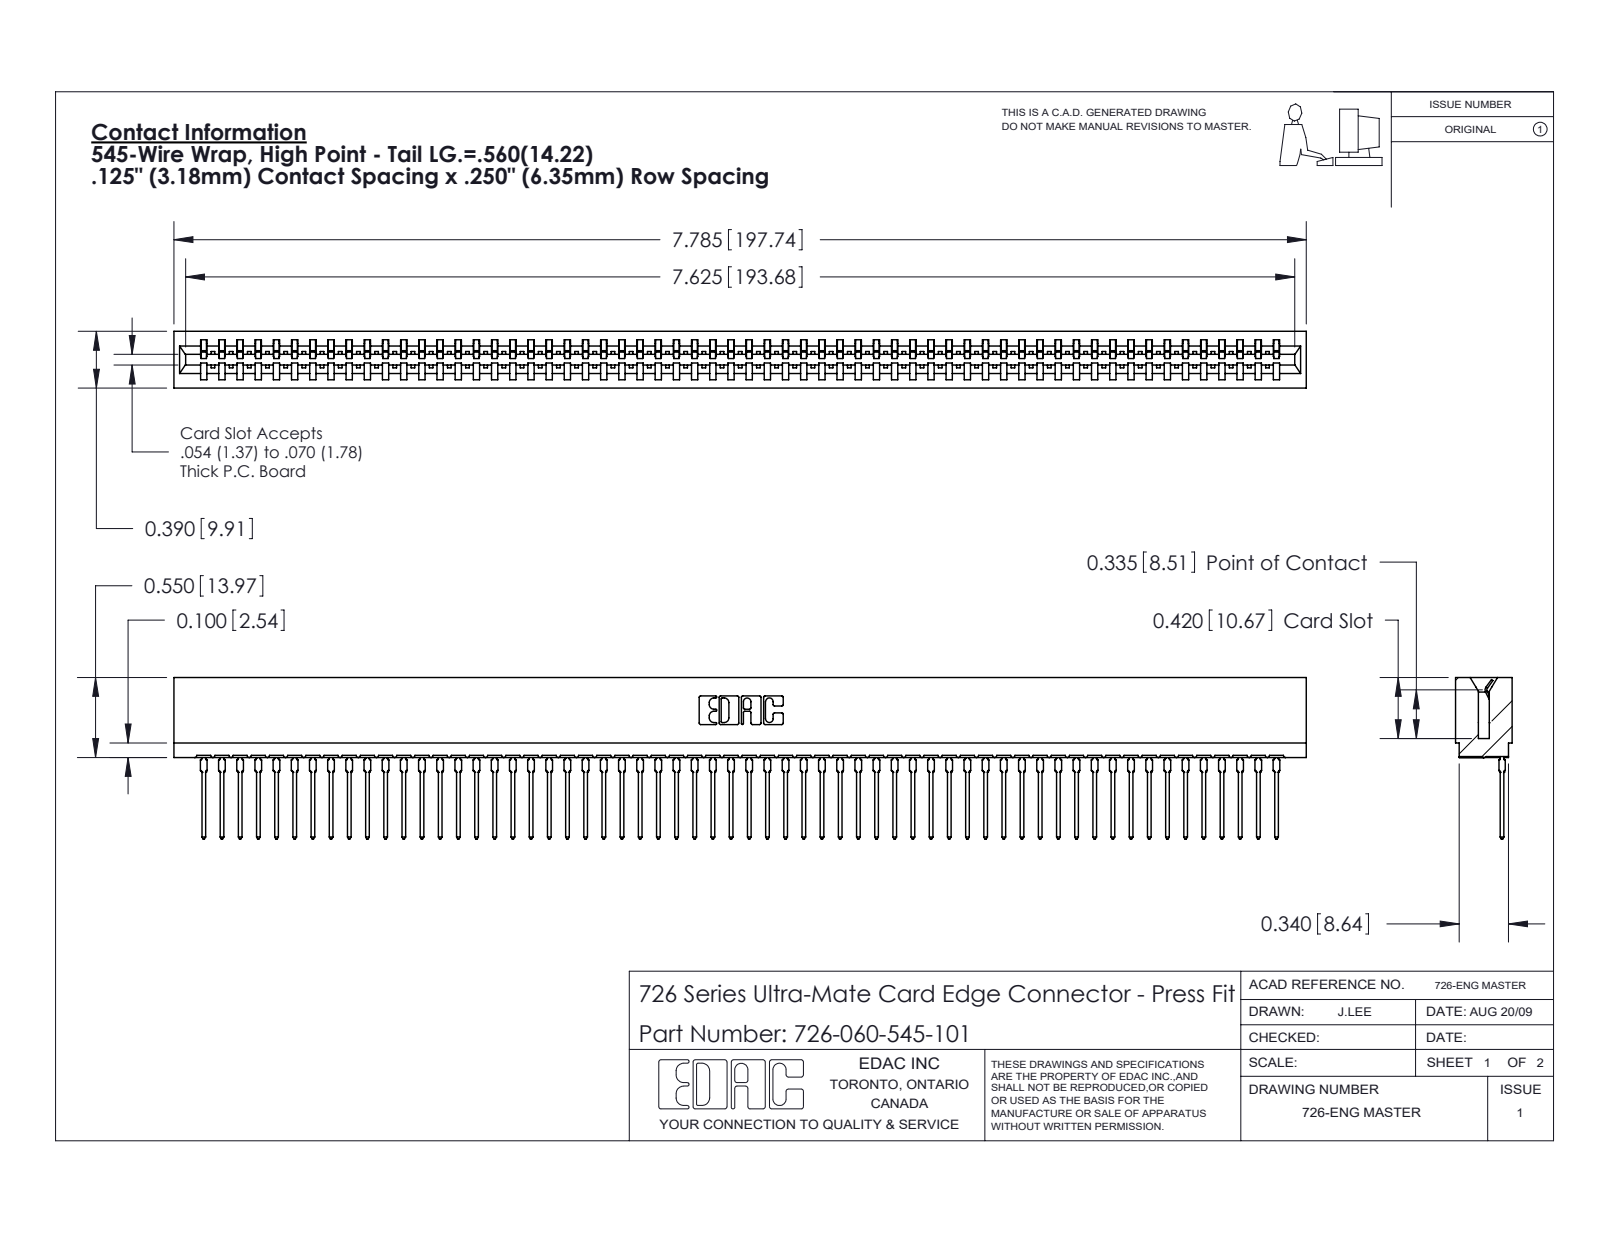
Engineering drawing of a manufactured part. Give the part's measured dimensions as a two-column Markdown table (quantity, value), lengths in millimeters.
| quantity | value |
| --- | --- |
| part name | 726-060-545-101; 746-292-001_545; 726 Part_.515 Slot Depth - 01 |
| STEP written by | SolidWorks 2020 (CONFIG_CONTROL_DESIGN) |
| units | millimeters |
| bodies | 61 solids, 6577 faces (3835 planar, 1182 cylindrical, 1560 other) |
| overall size | 197.7 × 28.2 × 9.9 |
| volume | 17 710 mm³ |
| surface area | 28 150 mm² |
| partial cylindrical surfaces (radius × count) | 0.5 × 120, 0.4 × 61, 0.3 × 22, 0.2 × 6, 0.8 × 6, 0.1 × 4, 0.3 × 4, 0.7 × 3 |
| main face-to-face distances | 1.4, 8.5, 9.9, 0.6, 7.8, 6.4, 2.1, 7, 9.3, 0.8 |
